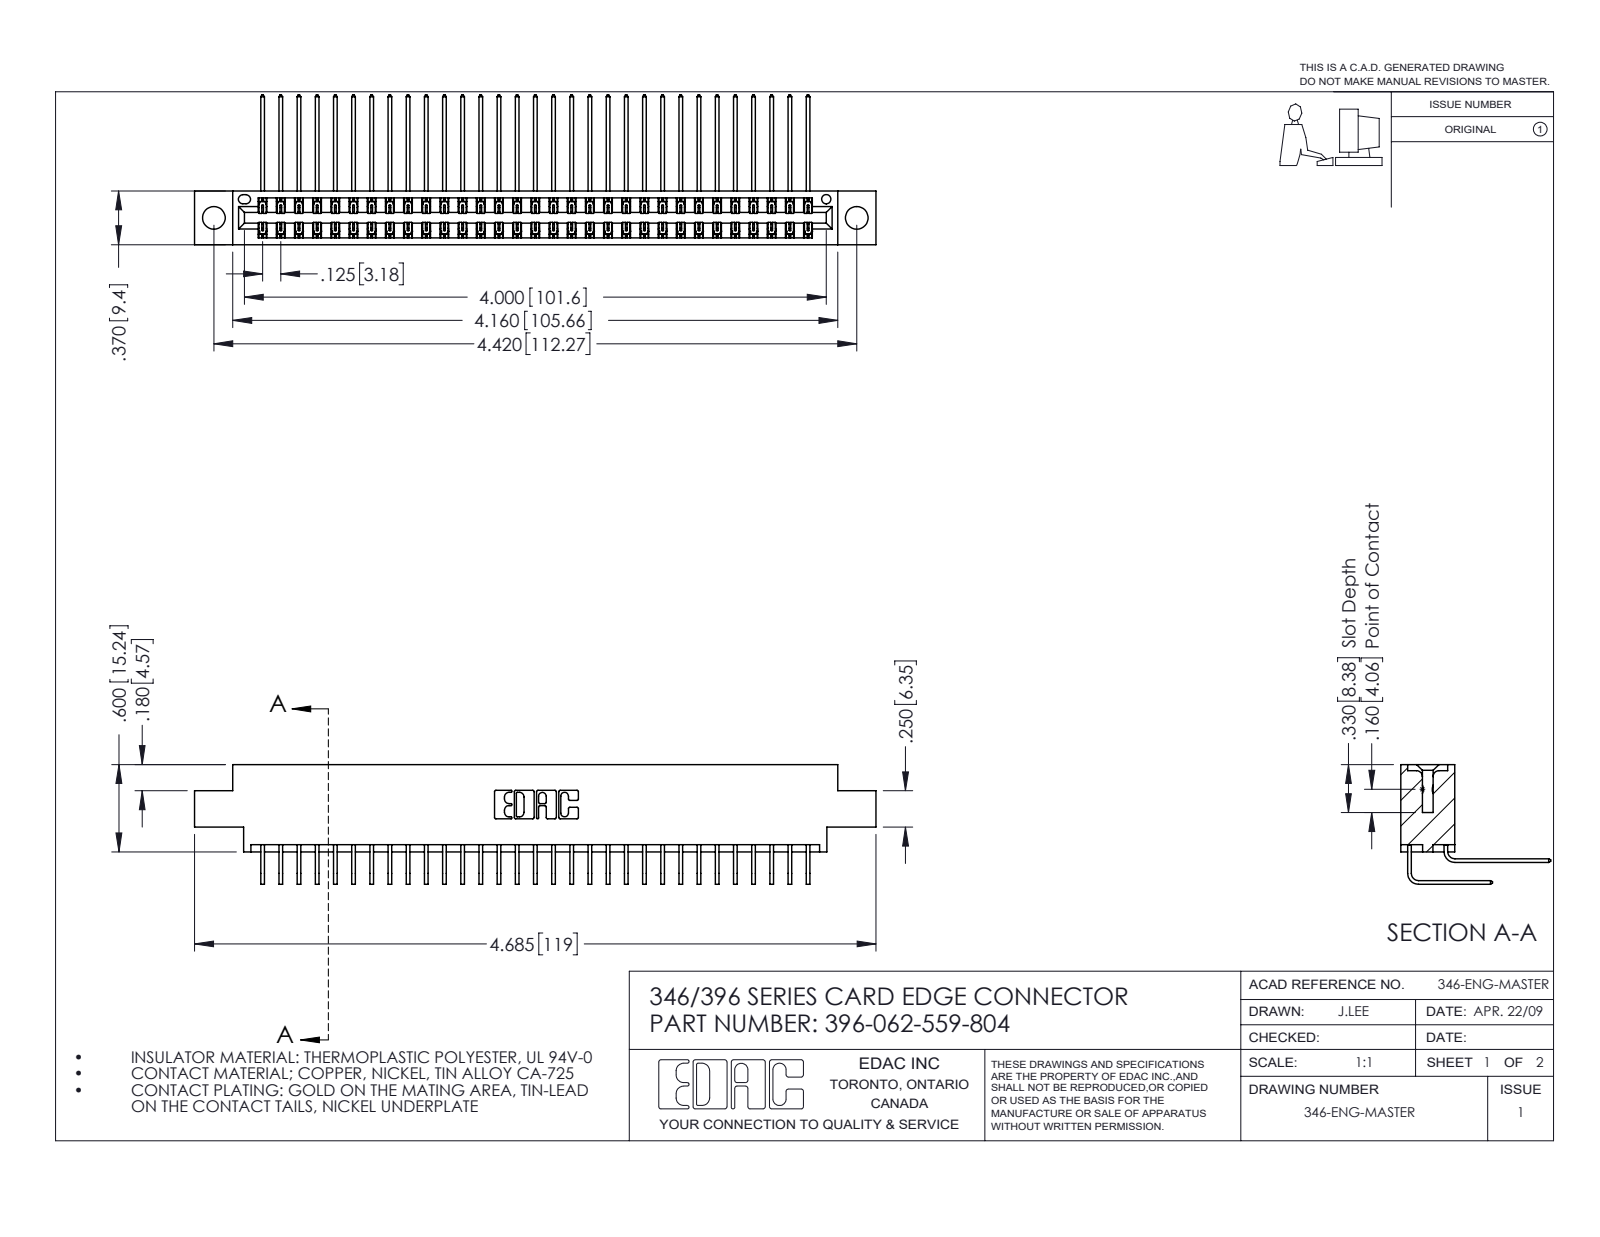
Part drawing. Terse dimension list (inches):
name: 396-062-559-804; 345-292-001_558 559 Tail - 1; 345-292-001_559 Tail - 2; 346 Part_0.170 Offset - 0.156 Dia-TH
written by: SolidWorks 2016 (CONFIG_CONTROL_DESIGN)
unit: in
bodies: 63 solids, 3474 faces (2374 planar, 1100 cylindrical, 0 other)
size: 4.685 × 1.03 × 0.823
volume: 0.71 in³; area: 27.17 in²
holes: 2× ⌀0.156, 1× ⌀0.064
rounds: 93× R0.006, 22× R0.01, 6× R0.007, 6× R0.031, 3× R0.026, 2× R0.014, 2× R0.022, 2× R0.024
face distances: 0.048, 0.322, 0.025, 0.37, 0.25, 0.072, 0.298, 0.275, 0.148, 0.222
hole spacings: 0.246, 4.212, 4.42
